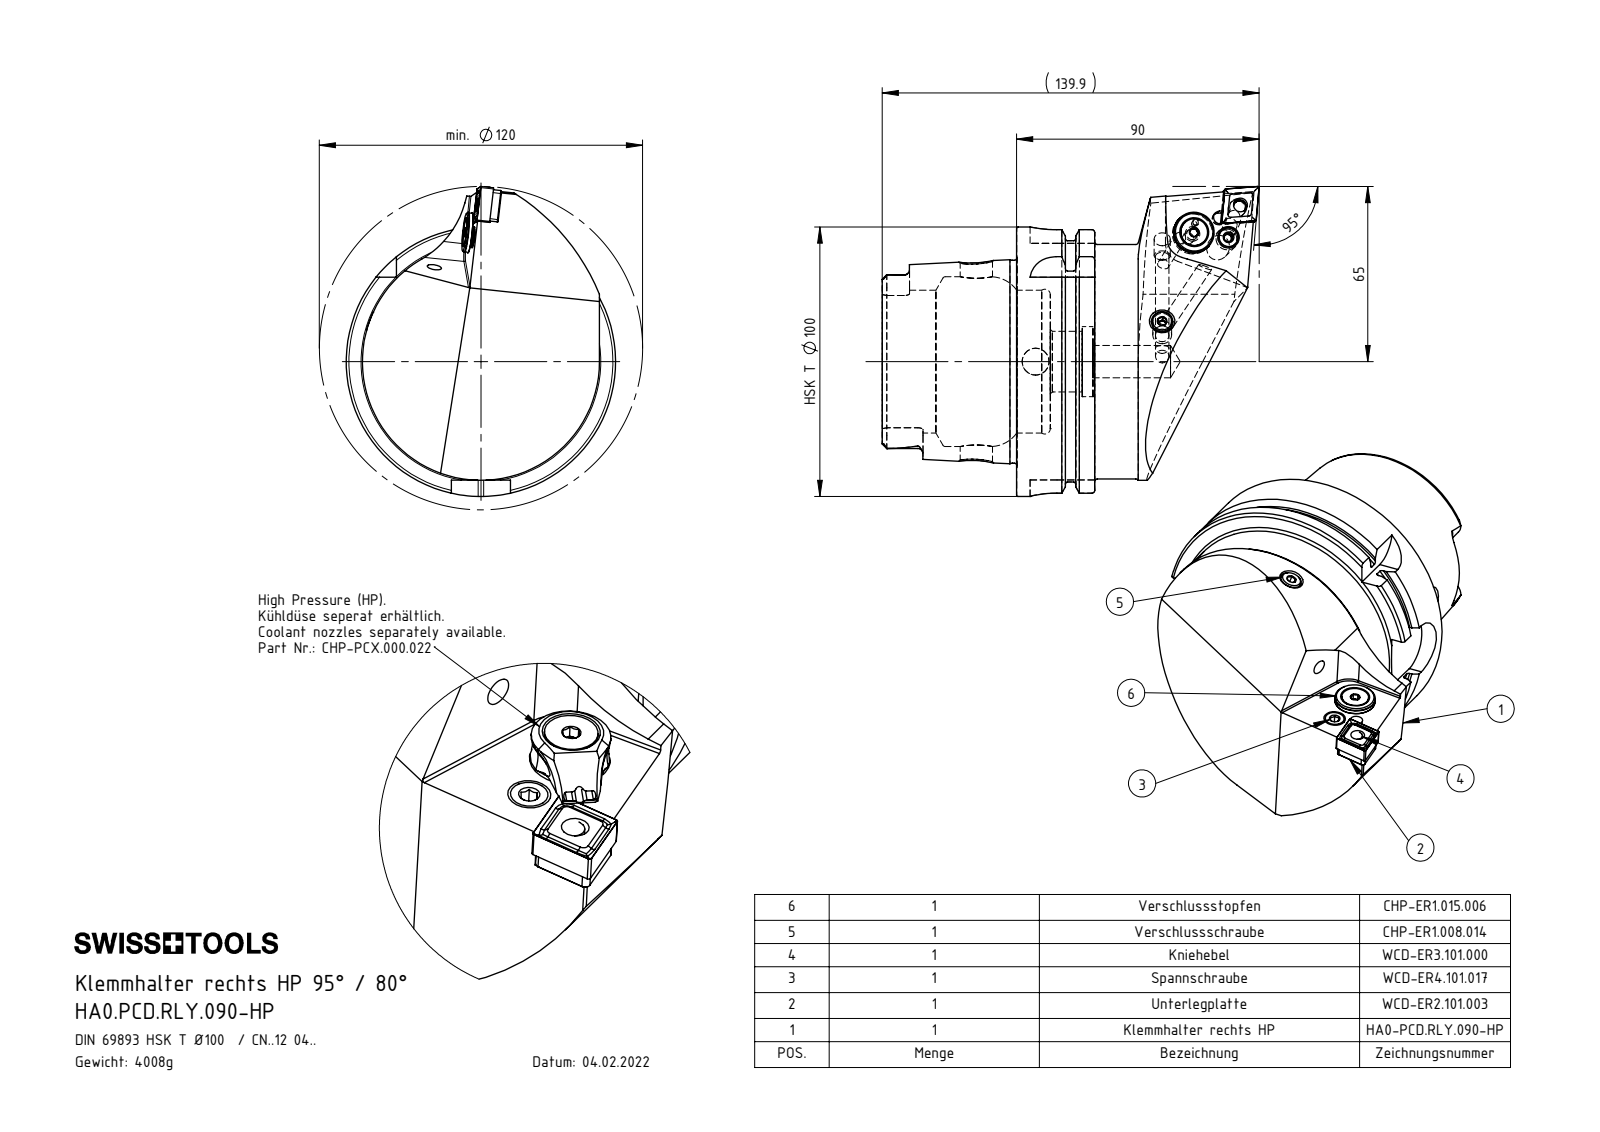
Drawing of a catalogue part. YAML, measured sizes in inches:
part_name: "CHP-ER1.015.006_A; DIN 7991 - M5x15; CHP-ER1.008.014_A; CHP-ER1.015.006 (+8 more)"
step_written_by: "SolidWorks 2017 (AUTOMOTIVE_DESIGN)"
units: inches
bodies: {solids: 12, faces: 509, planar: 156, cylindrical: 144, other: 209}
overall_size: [5.508, 4.528, 3.937]
volume: 31.1
surface_area: 111.8
round_holes:
  - {diameter: 0.197, count: 4}
  - {diameter: 0.165, count: 2}
  - {diameter: 0.276, count: 2}
  - {diameter: 0.472, count: 2}
  - {diameter: 0.047, count: 1}
  - {diameter: 0.079, count: 1}
  - {diameter: 0.098, count: 1}
  - {diameter: 0.118, count: 1}
  - {diameter: 0.203, count: 1}
  - {diameter: 0.205, count: 1}
  - {diameter: 0.236, count: 1}
  - {diameter: 0.252, count: 1}
round_bosses_or_shafts:
  - {diameter: 0.315, count: 2}
  - {diameter: 3.937, count: 1}
  - {diameter: 3.62, count: 1}
  - {diameter: 3.425, count: 1}
  - {diameter: 2.963, count: 1}
  - {diameter: 0.591, count: 1}
  - {diameter: 0.528, count: 1}
  - {diameter: 0.394, count: 1}
partial_cylinders:
  - {radius: 0.075, count: 6}
  - {radius: 0.016, count: 4}
  - {radius: 0.039, count: 4}
  - {radius: 0.394, count: 4}
  - {radius: 0.02, count: 2}
  - {radius: 0.098, count: 2}
  - {radius: 0.19, count: 2}
  - {radius: 0.192, count: 2}
face_to_face_distances: [0.49, 1.14, 0.65, 1.965, 2.455, 3.104, 3.457, 3.079, 1.114, 0.624]
hole_center_spacings: [0.177, 0.089, 0.516, 0.52, 0.682, 0.685, 0.8, 0.802]
